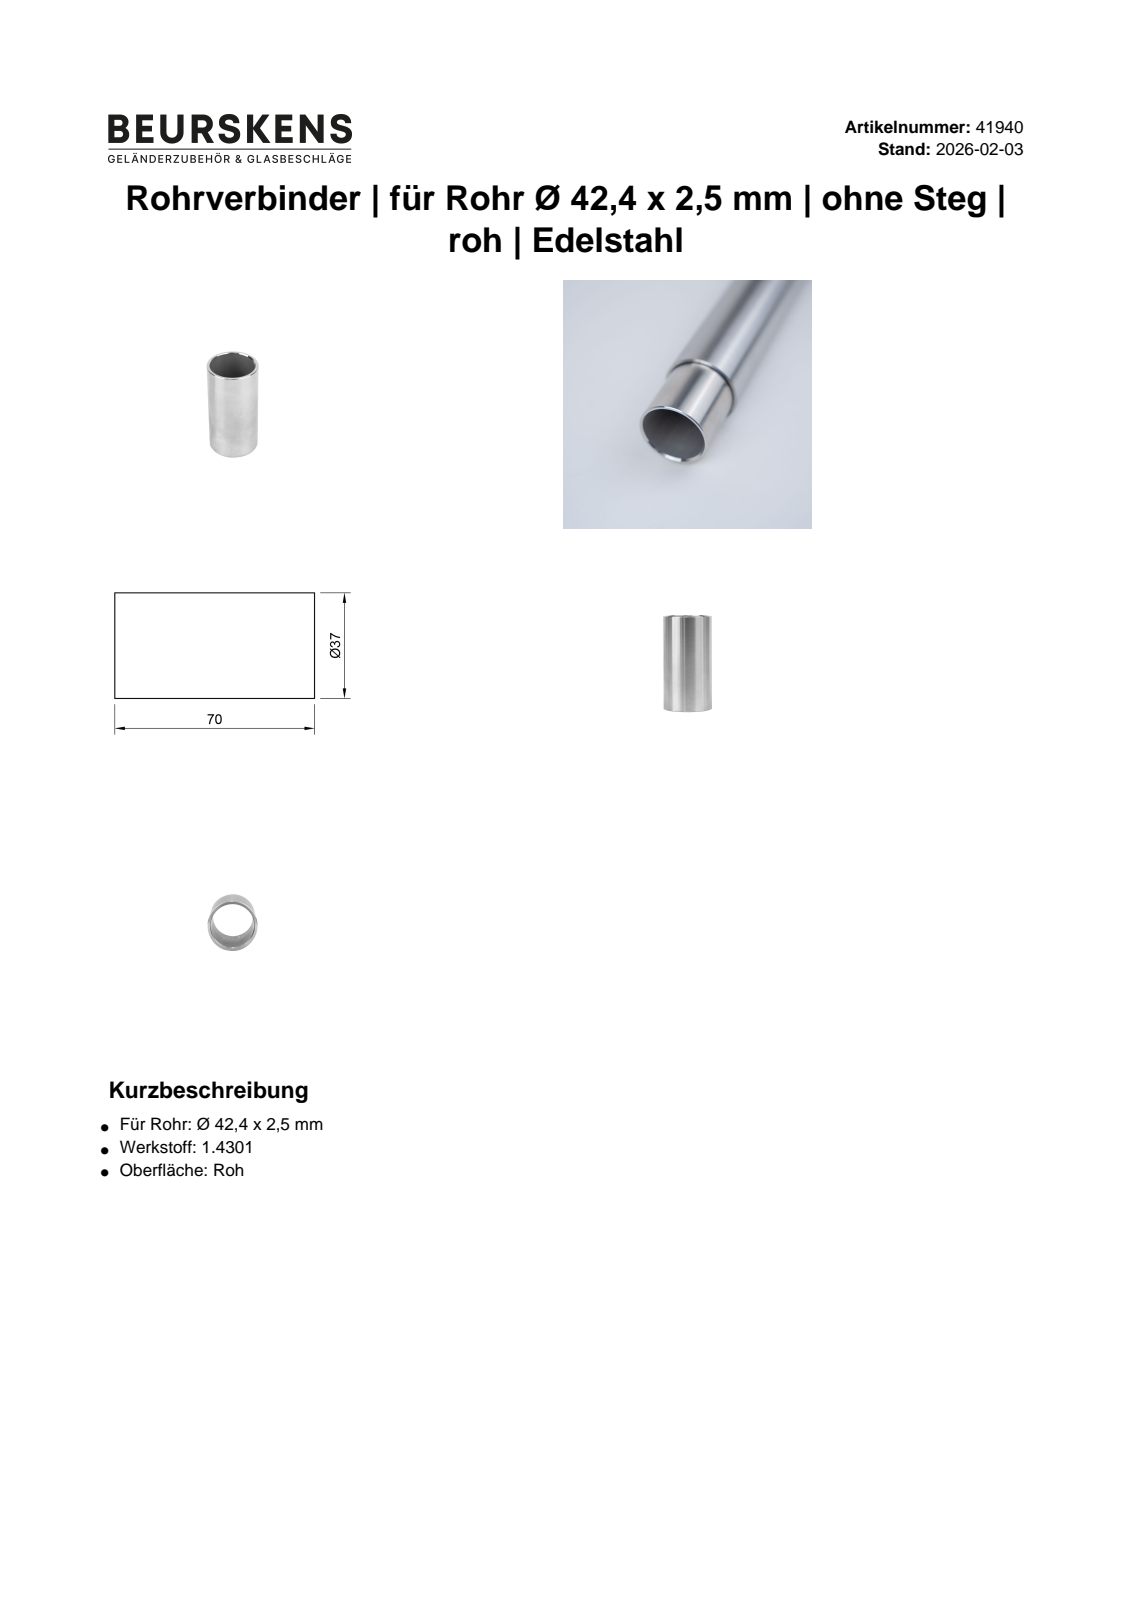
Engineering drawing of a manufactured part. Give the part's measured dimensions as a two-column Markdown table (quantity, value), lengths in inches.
| quantity | value |
| --- | --- |
| part name | 41940 |
| STEP written by | Autodesk Inventor 2022 (AUTOMOTIVE_DESIGN) |
| units | inches |
| bodies | 1 solid, 4 faces (2 planar, 2 cylindrical, 0 other) |
| overall size | 2.756 × 1.457 × 1.457 |
| volume | 0.245 in³ |
| surface area | 25.06 in² |
| round holes (diameter × count) | 1.417 × 1 |
| round bosses / shafts (diameter × count) | 1.457 × 1 |
| main face-to-face distances | 2.756 |
